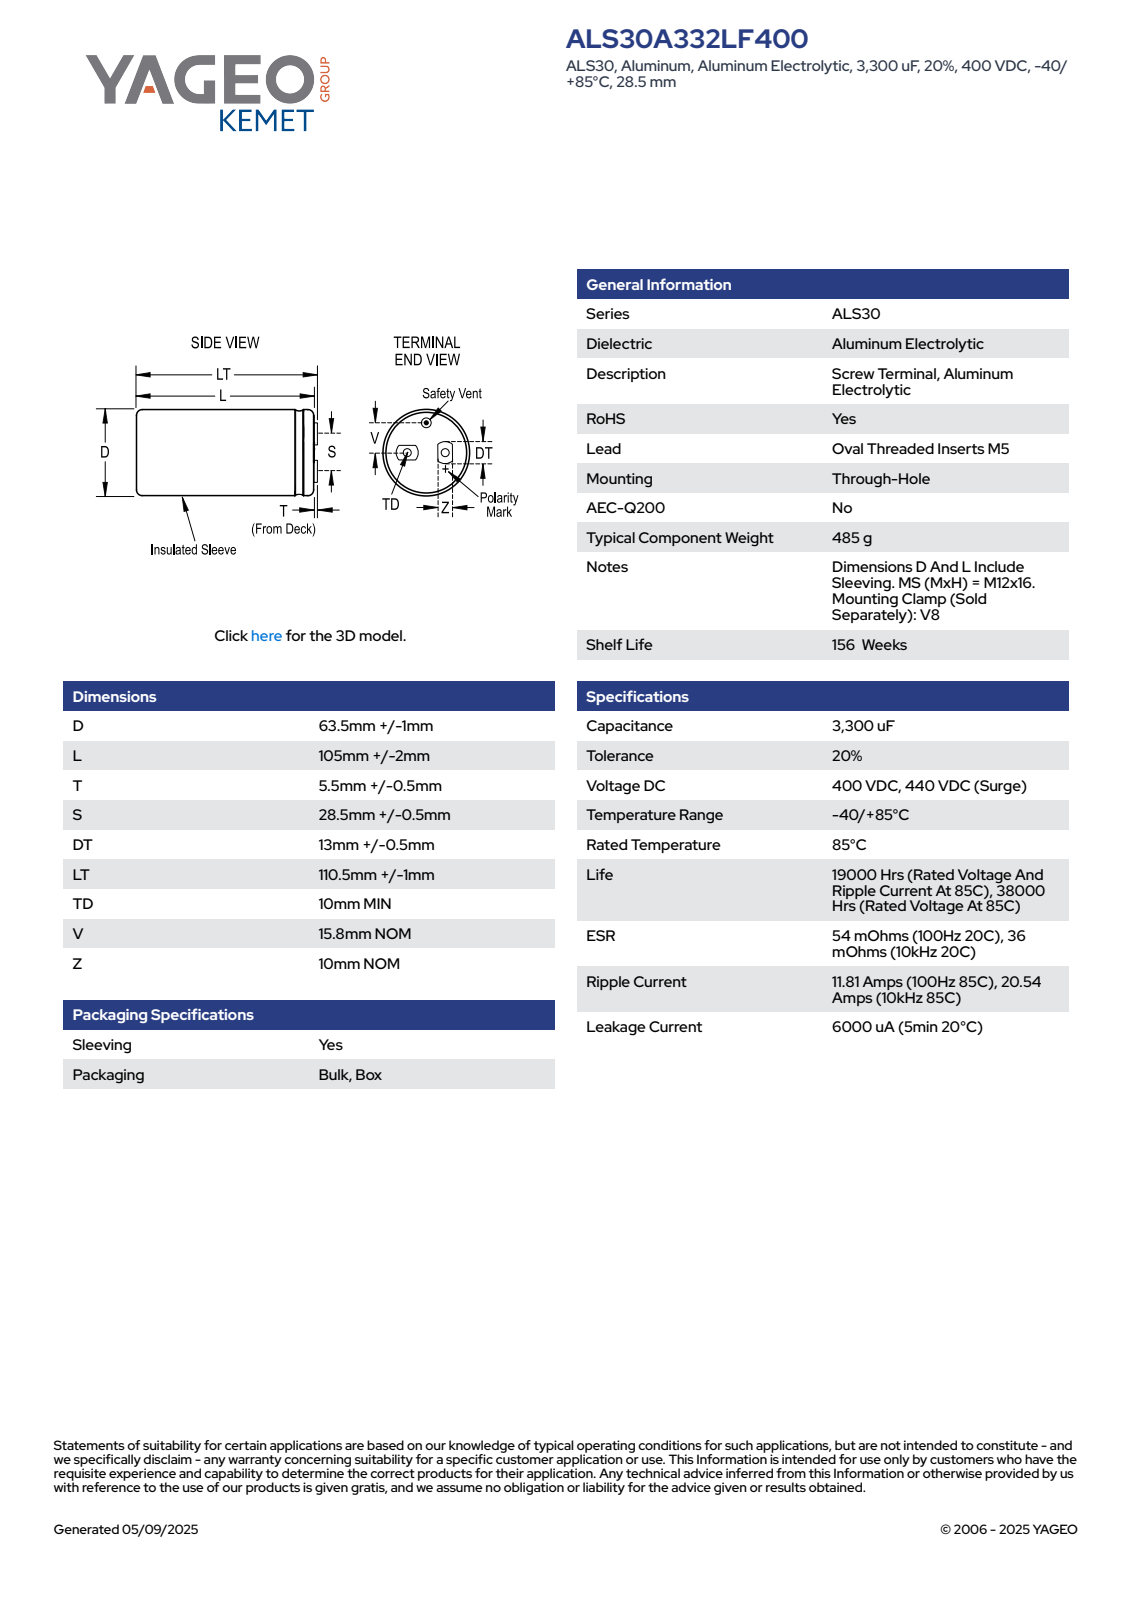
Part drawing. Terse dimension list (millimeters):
name: CARC_KALSO_63.5X105_D64.5L107T6S28.5LT111.50V15.800
written by: SolidWorks 2014 (AUTOMOTIVE_DESIGN)
unit: mm
bodies: 1 solid, 109 faces (40 planar, 30 cylindrical, 39 other)
size: 112 × 64.5 × 64.5
volume: 346 375 mm³; area: 29 366 mm²
holes: 2× ⌀5, 1× ⌀2, 1× ⌀60.5
bosses: 2× ⌀17, 1× ⌀64.5, 1× ⌀3
rounds: 4× R8, 1× R32.24
face distances: 106, 106.5, 0.5, 112, 6, 5.5, 10, 102, 4, 4.5
hole spacings: 14.25, 21.28, 15.8, 28.5
